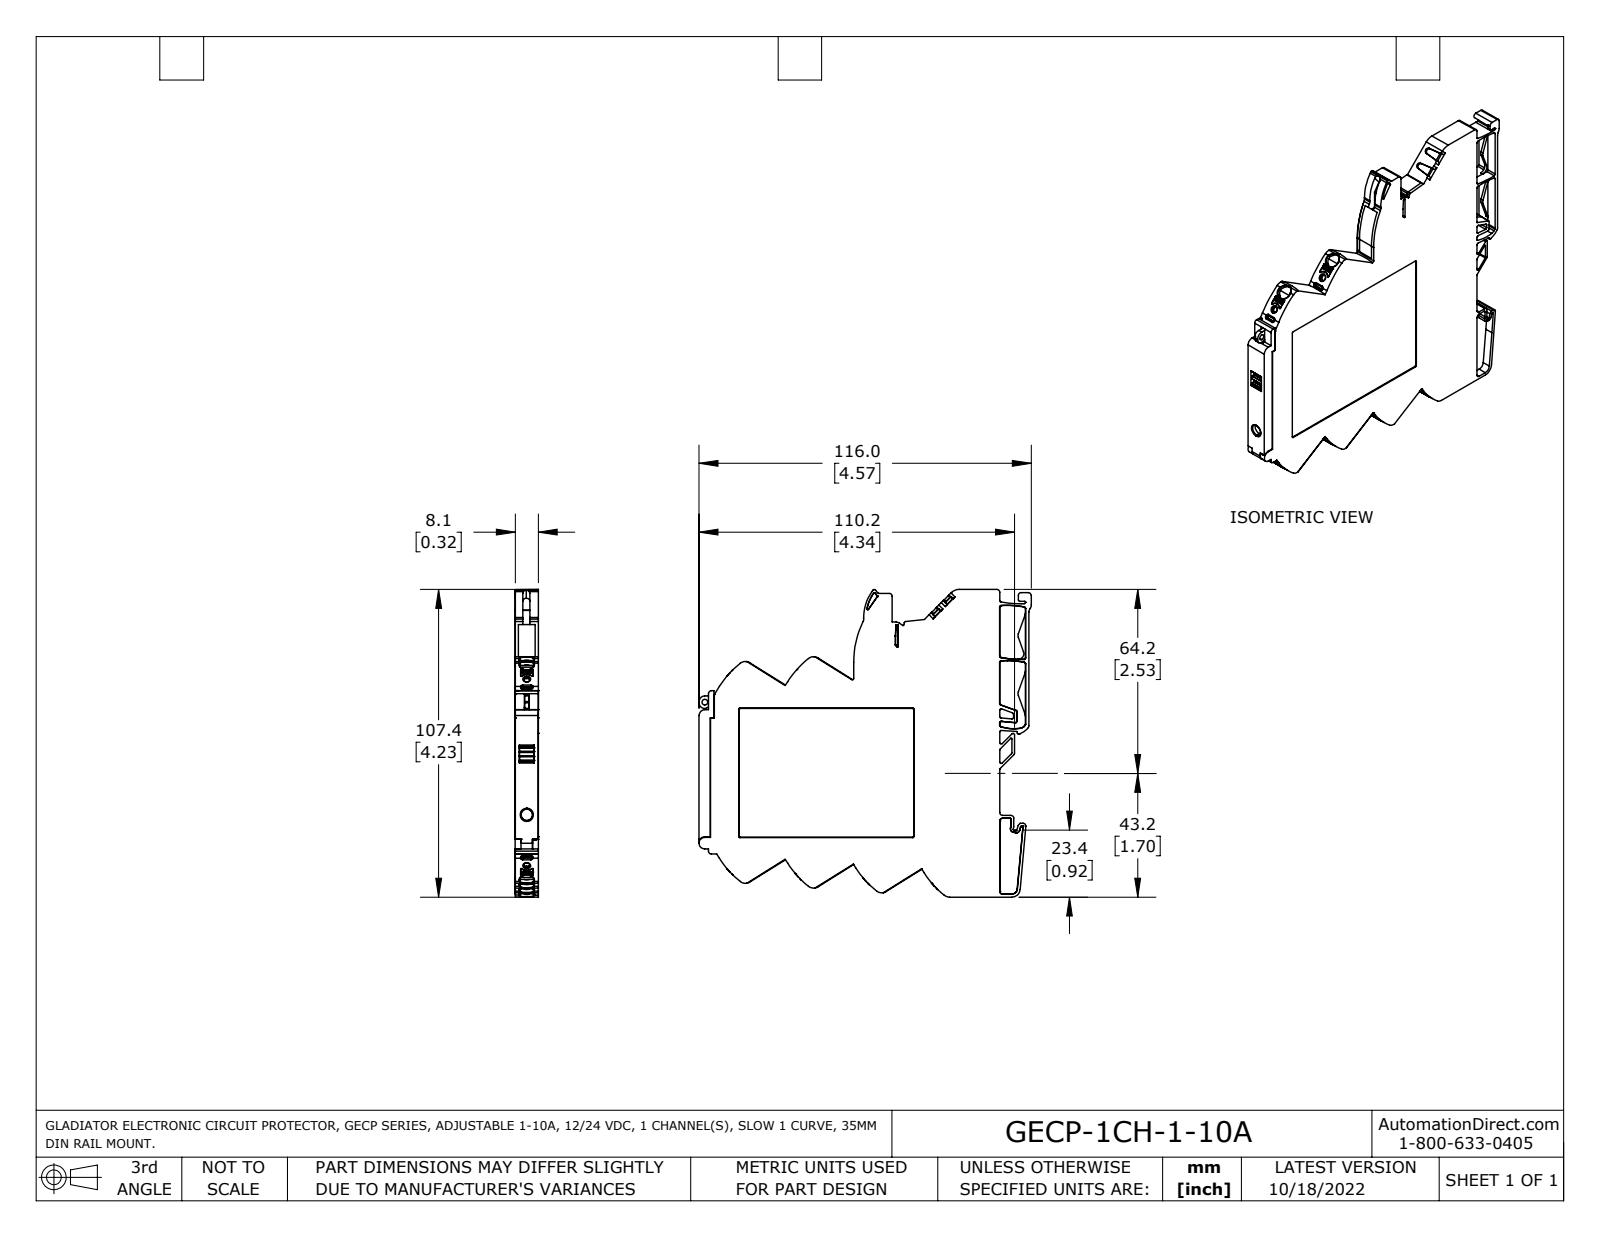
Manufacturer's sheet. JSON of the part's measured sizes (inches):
{"part_name": "GECP-1CH-1-10A", "step_written_by": "SolidWorks 2021 (AUTOMOTIVE_DESIGN)", "units": "inches", "bodies": {"solids": 1, "faces": 1182, "planar": 549, "cylindrical": 466, "other": 167}, "overall_size": [4.567, 4.241, 0.319], "volume_in3": 4.341, "surface_area_in2": 46.72, "round_holes": [[0.083, 6], [0.078, 1], [0.087, 1]], "round_bosses_or_shafts": [[0.083, 1]], "partial_cylinders_radius": [[0.02, 58], [0.039, 45], [0.008, 43], [0.01, 28], [0.012, 27], [0.079, 13], [0.009, 12], [1.299, 12]], "face_to_face_distances": [0.319, 0.311, 0.309, 0.317, 0.201, 0.157, 0.118, 0.354, 3.935, 4.093], "hole_center_spacings": [0.559, 1.118, 0.559, 1.677, 1.937]}
